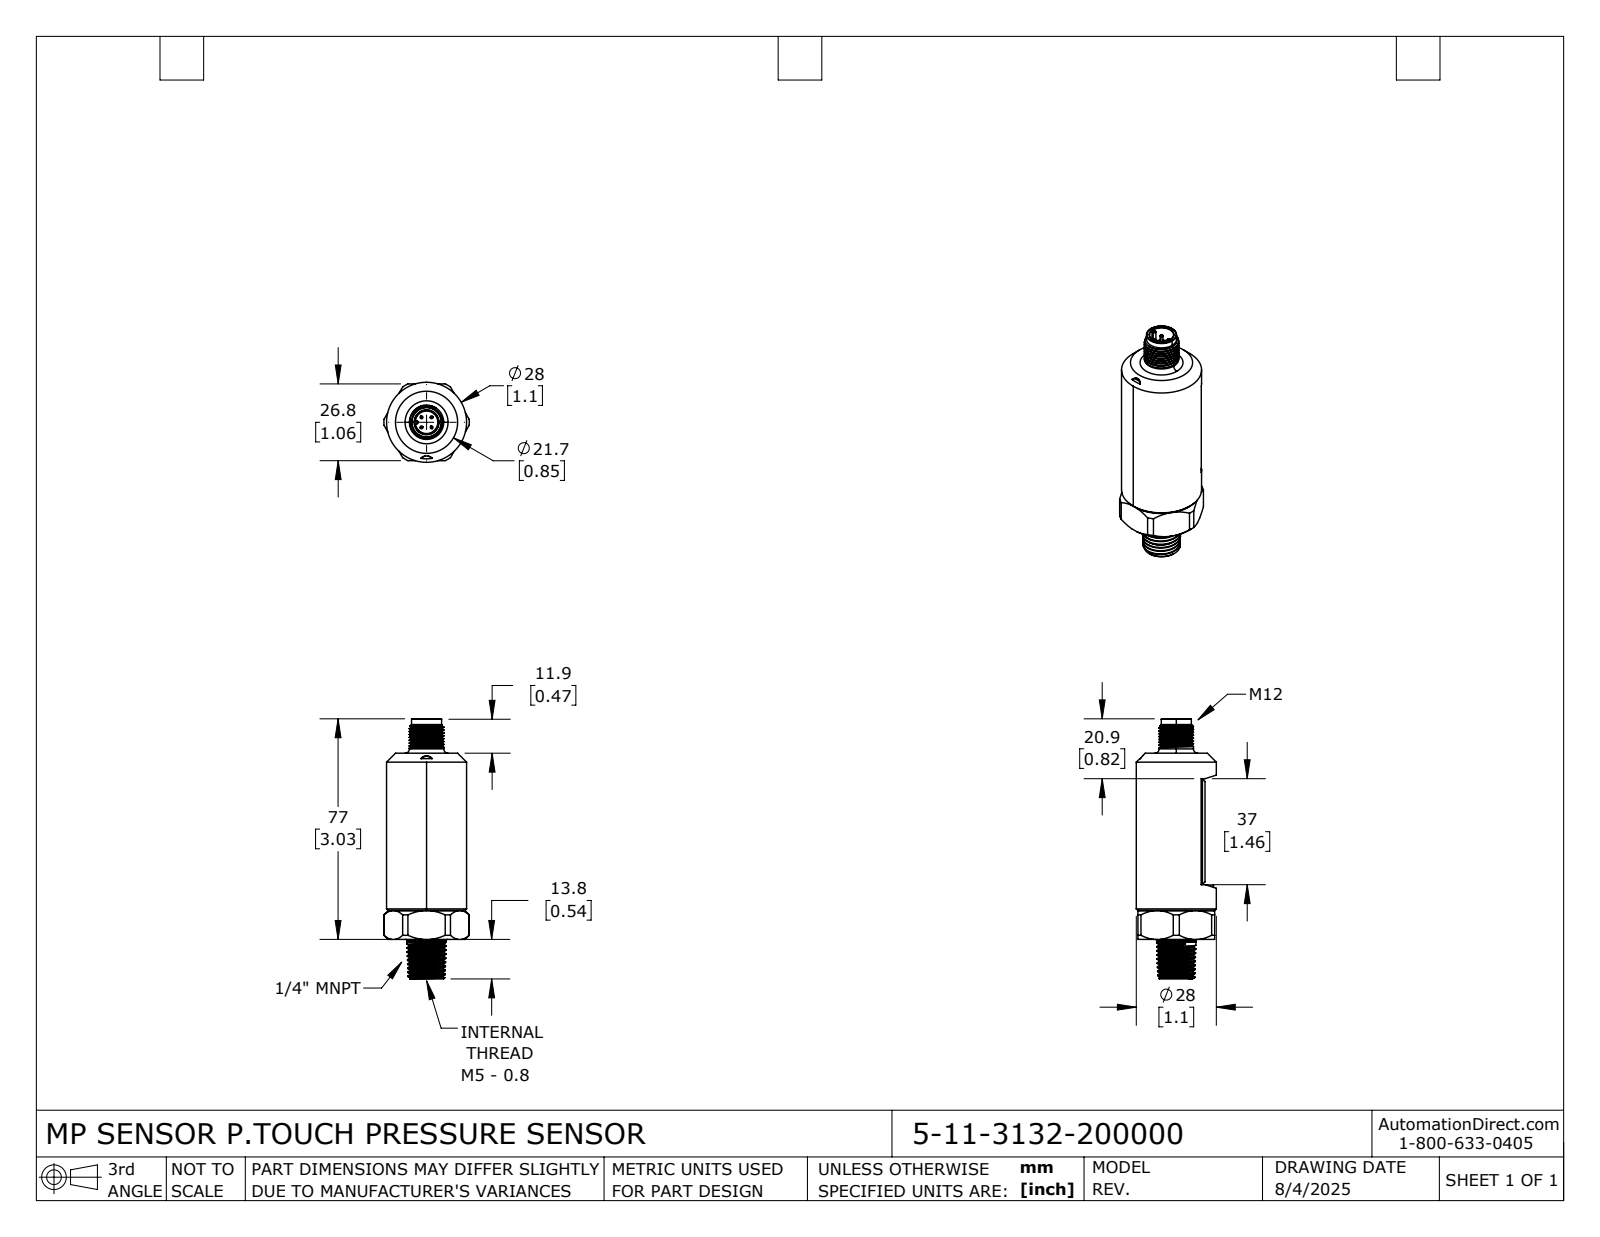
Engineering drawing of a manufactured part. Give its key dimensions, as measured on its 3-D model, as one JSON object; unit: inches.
{"part_name": "5-11-3132-200000", "step_written_by": "SolidWorks 2024 (AUTOMOTIVE_DESIGN)", "units": "inches", "bodies": {"solids": 1, "faces": 199, "planar": 46, "cylindrical": 68, "other": 85}, "overall_size": [3.575, 1.173, 1.1], "volume_in3": 2.423, "surface_area_in2": 13.82, "round_holes": [[0.079, 1], [0.165, 1], [0.331, 1]], "round_bosses_or_shafts": [[0.039, 4], [1.1, 1], [1.024, 1], [0.539, 1], [0.472, 1], [0.413, 1]], "partial_cylinders_radius": [[0.006, 2], [0.092, 1], [0.587, 1]], "face_to_face_distances": [1.055, 2.559, 0.922, 0.133, 0.543, 3.102, 0.354, 1.811, 0.35, 0.186]}
